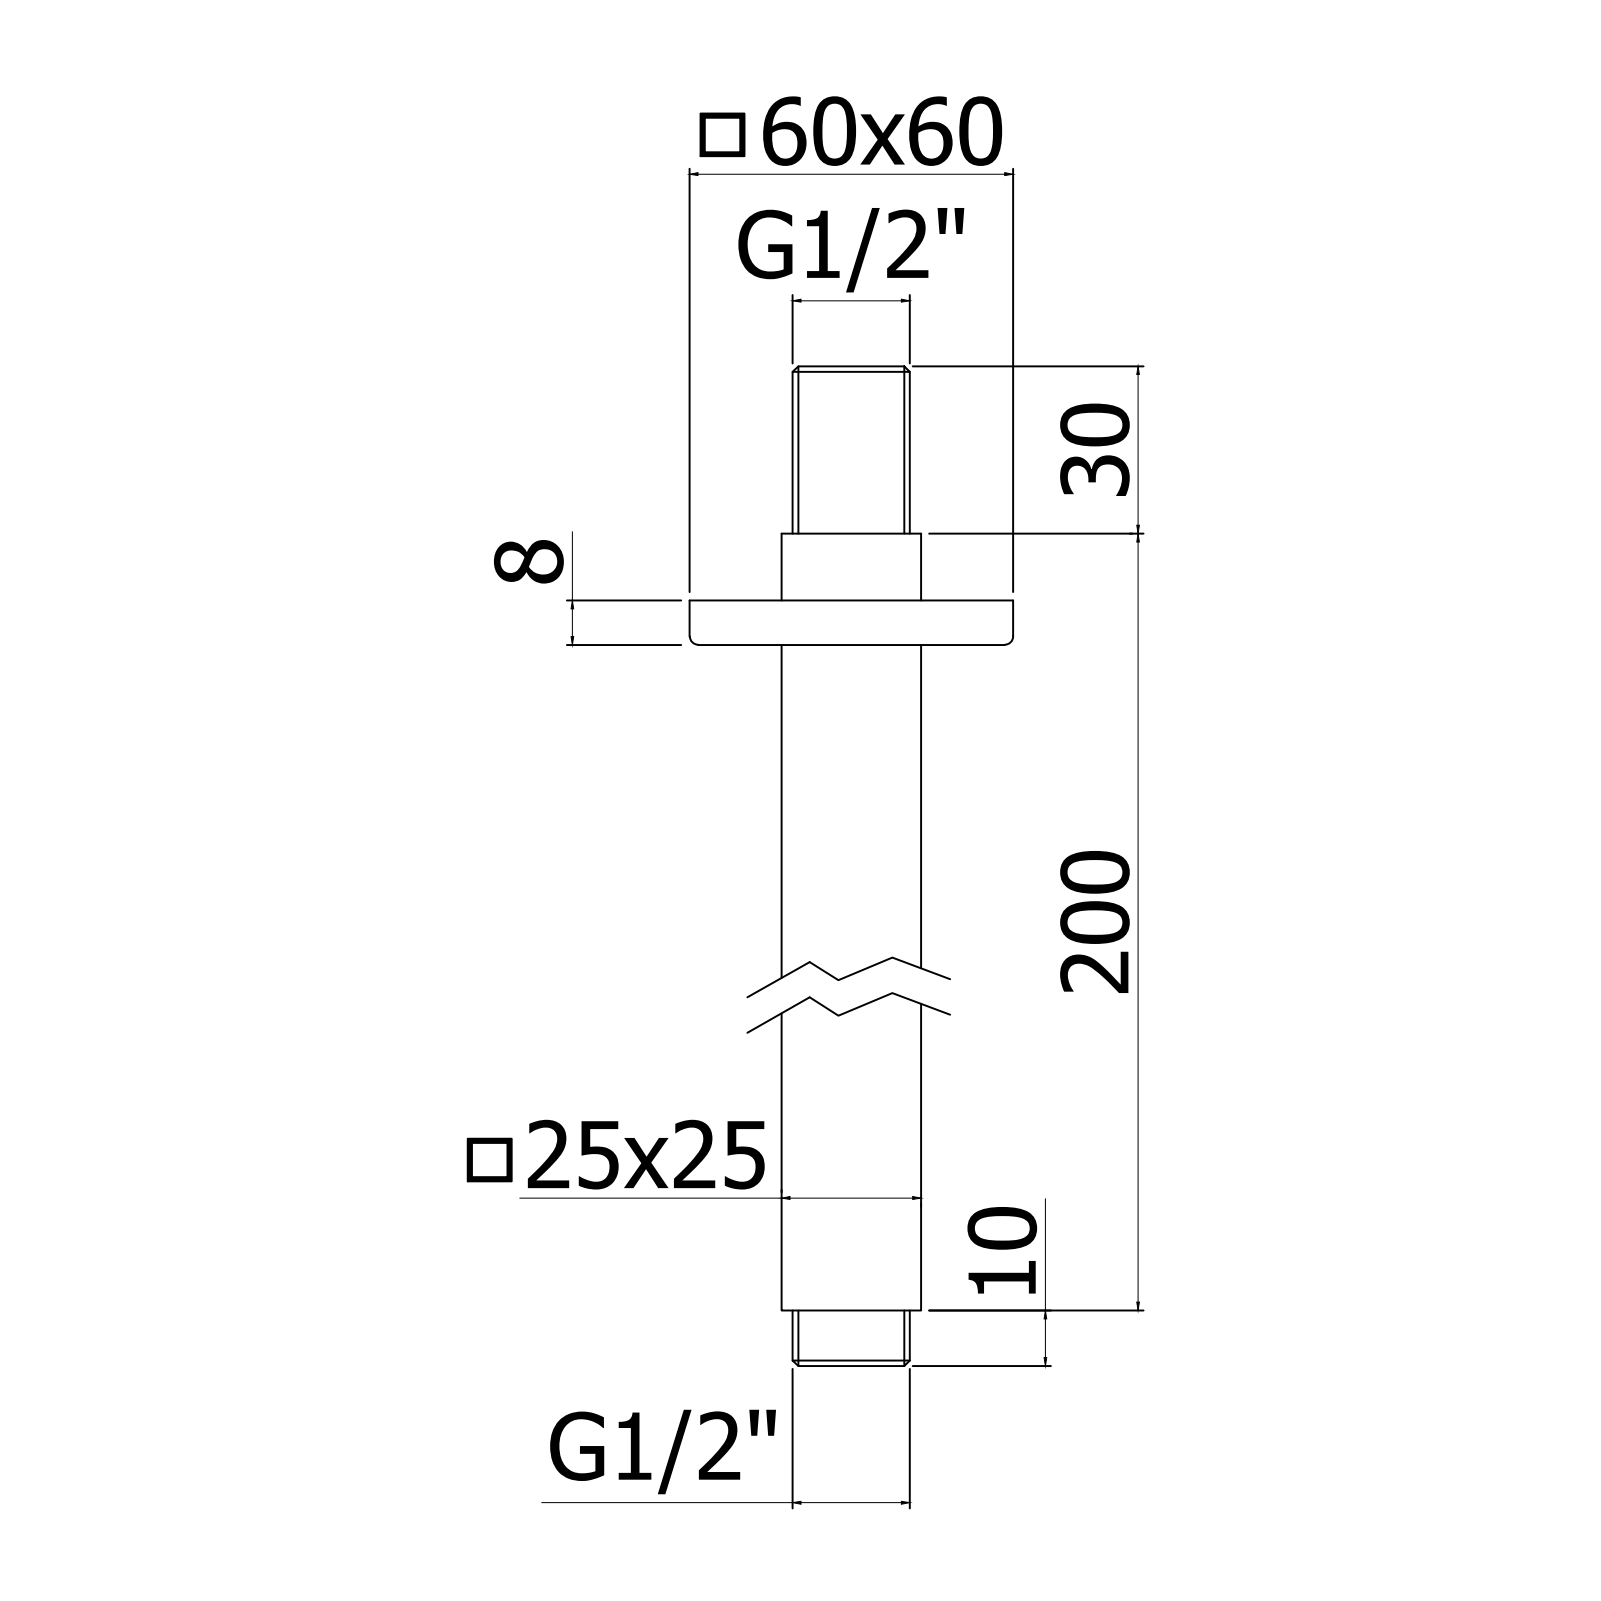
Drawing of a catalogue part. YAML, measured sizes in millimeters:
part_name: "ZSOF119CR"
step_written_by: "CREO PARAMETRIC BY PTC INC, 2020044 (CONFIG_CONTROL_DESIGN)"
units: millimeters
bodies: {solids: 1, faces: 21, planar: 13, cylindrical: 4, other: 4}
overall_size: [210, 60, 60]
volume: 151961
surface_area: 29113
round_bosses_or_shafts:
  - {diameter: 21, count: 1}
  - {diameter: 17, count: 1}
face_to_face_distances: [25, 8, 17.5, 42.5, 60, 192, 200, 202, 10, 210]
